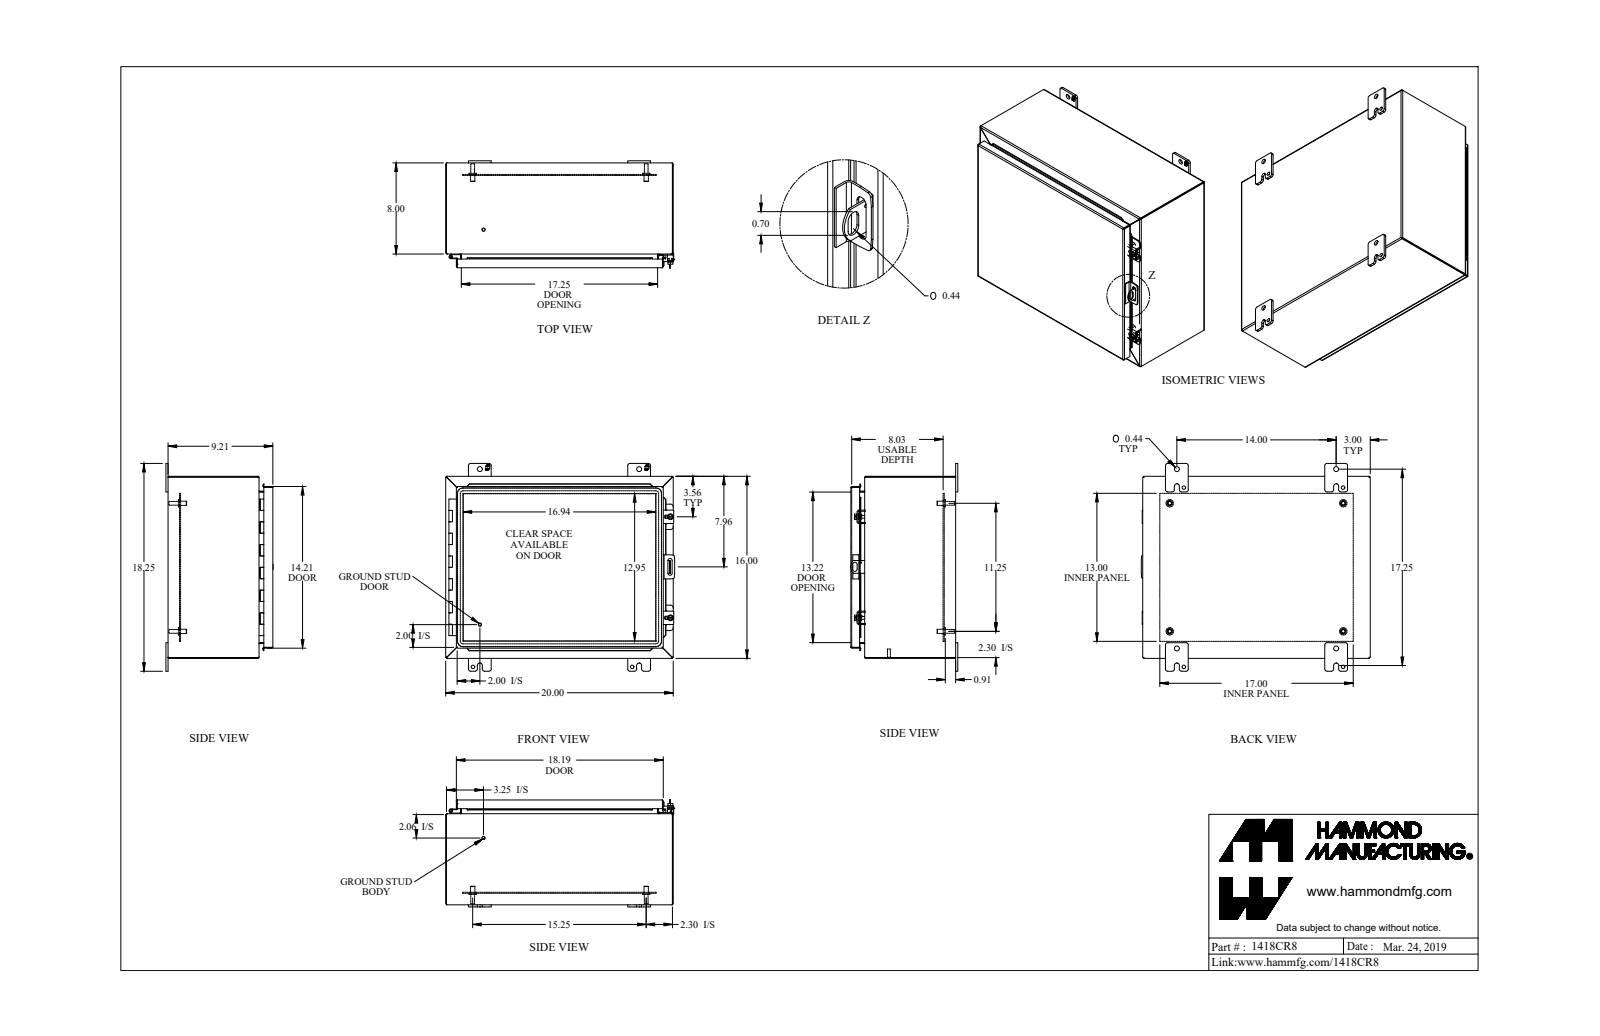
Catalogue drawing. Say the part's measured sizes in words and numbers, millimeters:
The part is named "1418CR8". Its 3-D file was written by "SolidWorks 2019 (AUTOMOTIVE_DESIGN)". It is 26 solids with 870 faces: 588 planar, 226 cylindrical and 56 other. Overall it measures 510.4 by 463.6 by 239.7 millimeters. Its volume is 2 196 000 cubic millimeters and its surface area 2 252 000 square millimeters. Round holes: 4 of diameter 8, 4 of diameter 11.1, 4 of diameter 12.7, 2 of diameter 5.4, 1 of diameter 3.2, 1 of diameter 4.7. Round bosses or shafts: 4 of diameter 16.5, 4 of diameter 9.5, 4 of diameter 8.4, 2 of diameter 9.9, 2 of diameter 8, 2 of diameter 6.4, 1 of diameter 7.3. Partial cylindrical surfaces (rounded edges, fillets, slot ends): 25 of radius 1.2, 24 of radius 4.8, 13 of radius 3.6, 12 of radius 3, 8 of radius 0.2, 8 of radius 0.9, 8 of radius 1.1, 8 of radius 2. The main face-to-face distances are 1.8, 231.5, 229.6, 404.6, 233.3, 506.2, 2.4, 207.7, 205.8, 23.8. The hole center spacings are 355.6, 44.1, 400.1, 535.3, 285.8, 324.2, 342.6, 359.1.
